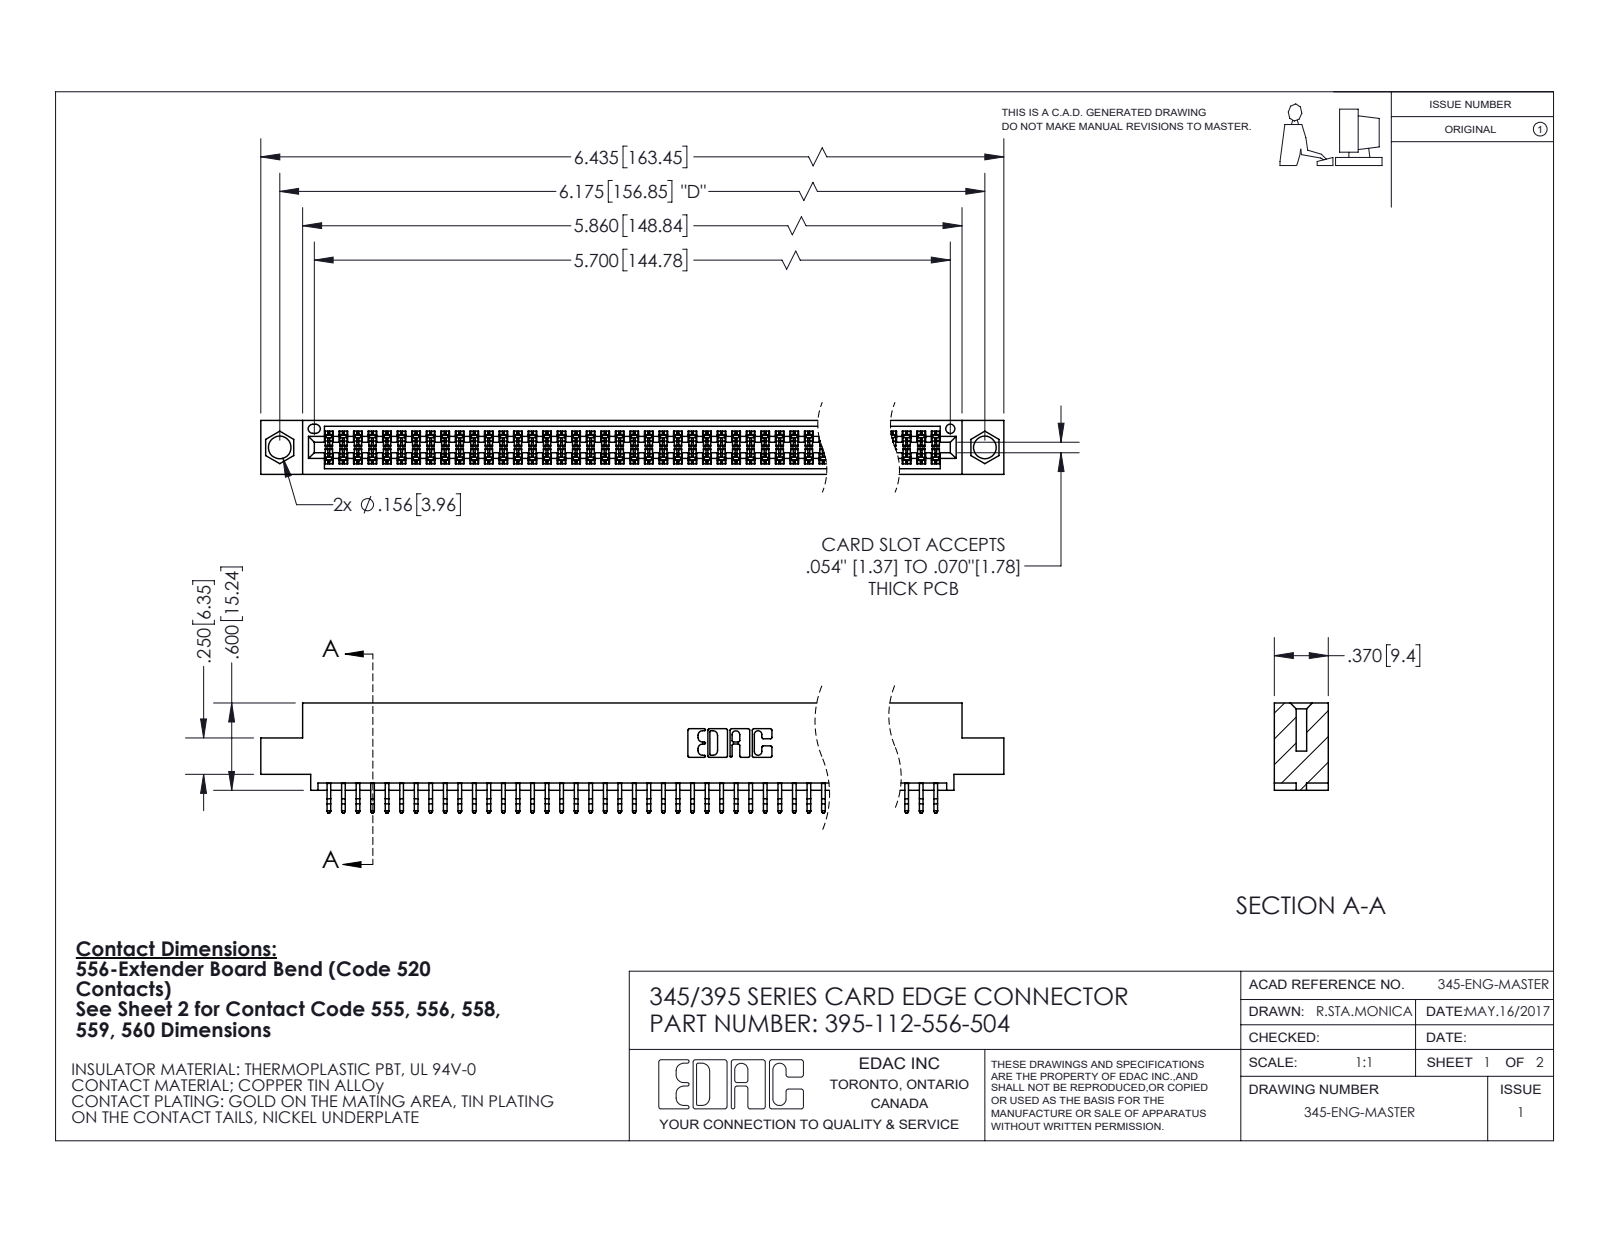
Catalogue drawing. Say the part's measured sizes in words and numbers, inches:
The part is named "345 Part_0.110 Offset - 0.156 Dia-TI; 395-112-556-504; 345-292-001_556 Tail". Its 3-D file was written by "SolidWorks 2020 (CONFIG_CONTROL_DESIGN)". It is 113 solids with 6416 faces: 4242 planar, 2174 cylindrical and 0 other. Overall it measures 6.435 by 0.757 by 0.37 inches. Its volume is 0.966 cubic inches and its surface area 36.44 square inches. Round holes: 2 of diameter 0.156, 1 of diameter 0.064. Partial cylindrical surfaces (rounded edges, fillets, slot ends): 224 of radius 0.006, 22 of radius 0.01, 6 of radius 0.007, 6 of radius 0.031, 3 of radius 0.026, 2 of radius 0.01, 2 of radius 0.014, 2 of radius 0.019. The main face-to-face distances are 0.298, 0.072, 0.37, 0.2, 0.025, 0.098, 0.272, 0.225, 0.175, 0.149. The hole center spacings are 0.27, 5.939, 6.175.
